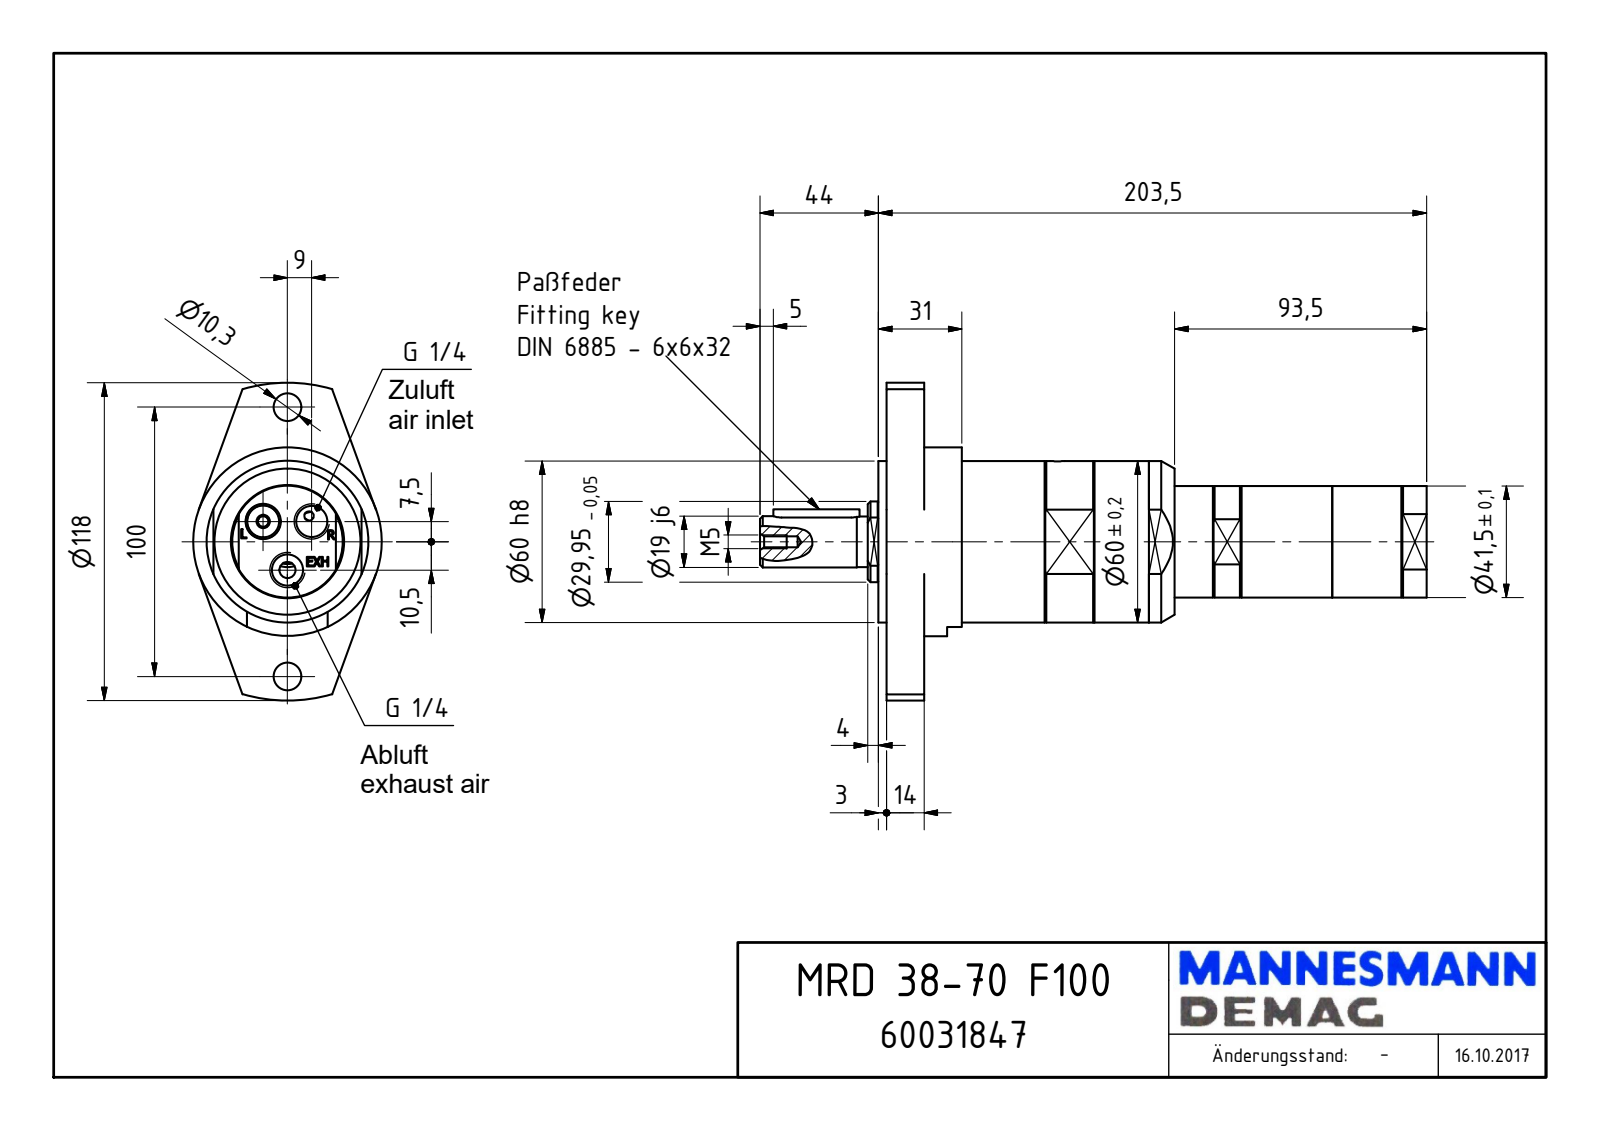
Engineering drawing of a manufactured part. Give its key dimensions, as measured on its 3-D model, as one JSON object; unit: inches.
{"part_name": "MRD 38-70 F100_60031847", "step_written_by": "Autodesk Inventor 2018 (AUTOMOTIVE_DESIGN)", "units": "inches", "bodies": {"solids": 1, "faces": 218, "planar": 130, "cylindrical": 42, "other": 46}, "overall_size": [9.744, 4.646, 2.756], "volume_in3": 30.64, "surface_area_in2": 83.01, "round_holes": [[0.451, 3], [0.157, 2], [0.406, 2], [0.061, 1], [0.163, 1], [0.217, 1], [1.378, 1], [1.575, 1], [1.654, 1]], "round_bosses_or_shafts": [[2.756, 1], [2.362, 1], [1.634, 1], [1.179, 1], [0.748, 1], [0.74, 1], [0.197, 1], [0.142, 1]], "partial_cylinders_radius": [[0.118, 2], [1.033, 1], [1.222, 1], [2.323, 1]], "face_to_face_distances": [0.551, 0.118, 0.669, 1.22, 3.661, 3.681, 7.343, 7.894, 8.012, 4.213], "hole_center_spacings": [0.461, 0.792, 1.71, 1.969, 2.291, 0.413, 0.709, 1.555]}
